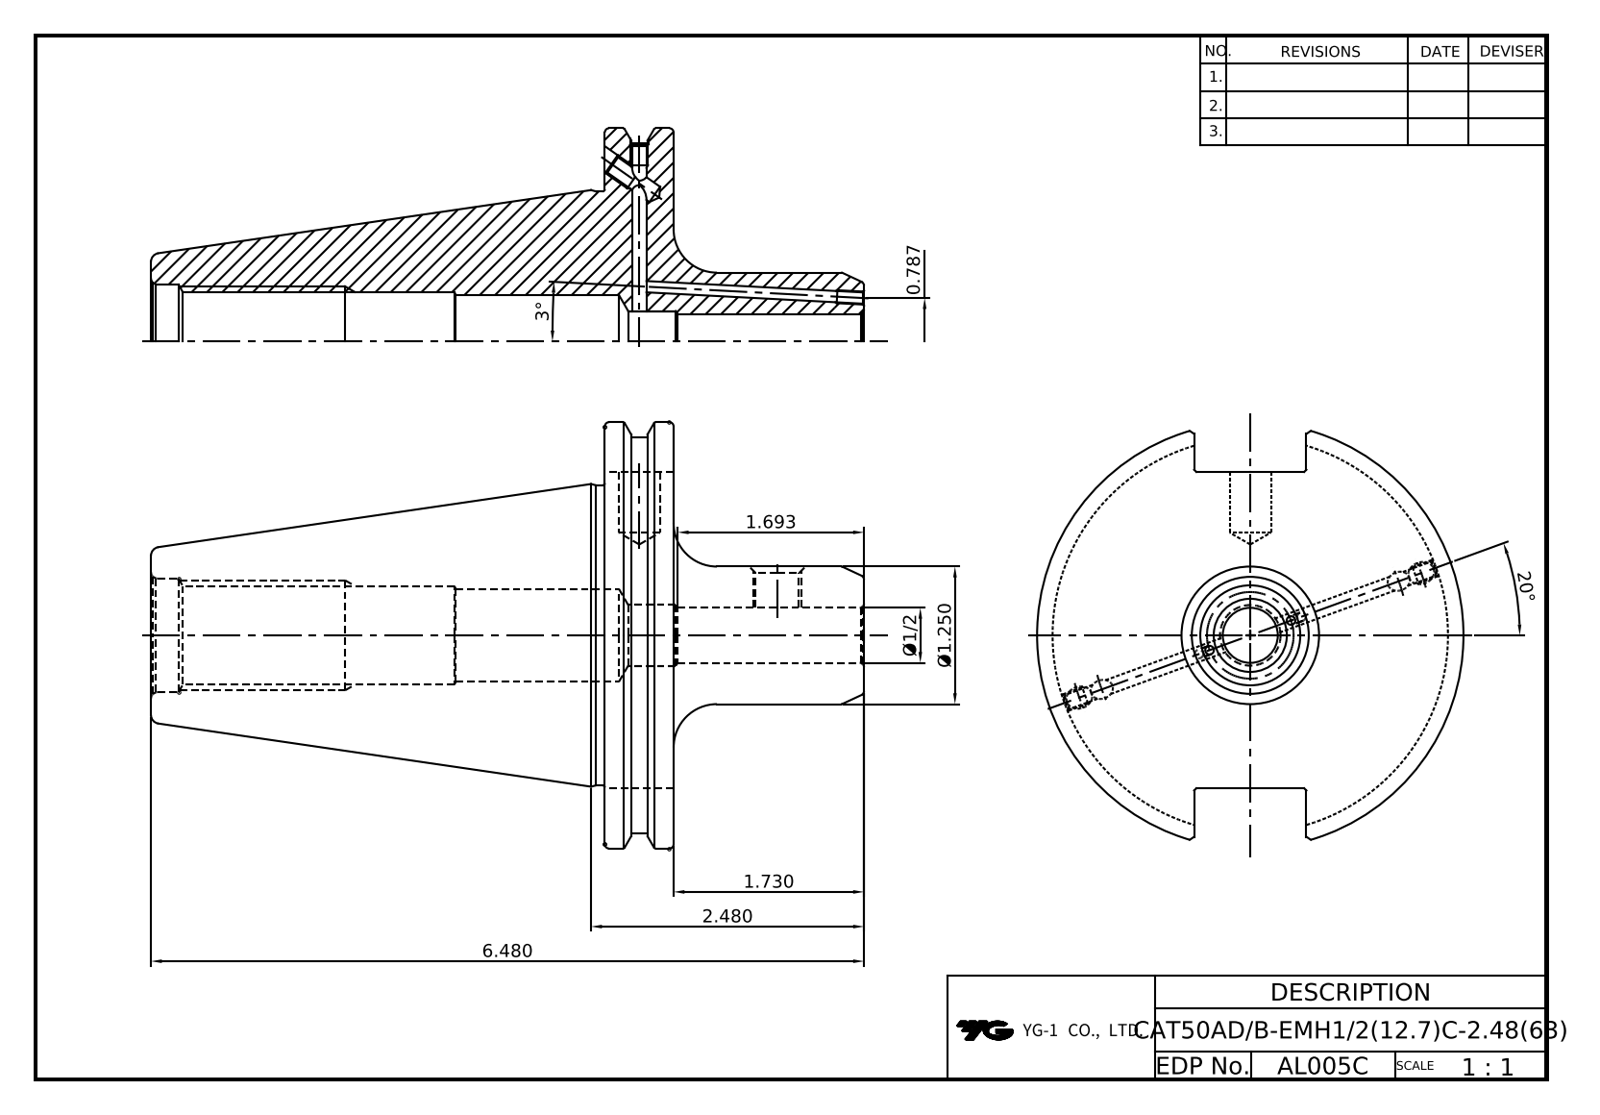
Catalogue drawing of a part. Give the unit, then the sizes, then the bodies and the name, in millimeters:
Units: millimetres
Overall size (bounding box): 164.6 × 98.42 × 94.69
Round holes (diameter × count): ⌀2.46 ×2, ⌀3.24 ×2, ⌀4.13 ×2, ⌀4.2 ×2, ⌀5 ×2, ⌀9.53 ×1, ⌀9.73 ×1, ⌀12.7 ×1, ⌀14 ×1, ⌀21.97 ×1, ⌀26.2 ×1
Round bosses / shafts (diameter × count): ⌀98.42 ×1, ⌀91.29 ×1, ⌀69.25 ×1, ⌀31.75 ×1
Main face-to-face distances: 15.88, 104.77, 120.65, 164.6, 59.83, 43.95, 73.03, 25.9, 114.64, 9.87
Hole centre spacings: 31.87
Volume: 349 254 mm³ · Surface area: 51 688 mm²
Bodies: 1 solid, 88 faces (36 planar, 28 cylindrical, 24 other)
Part name (STEP PRODUCT): LO-CAT50ADB-EMH12.7C-63
STEP written by: Autodesk Inventor 2025 (AUTOMOTIVE_DESIGN)
